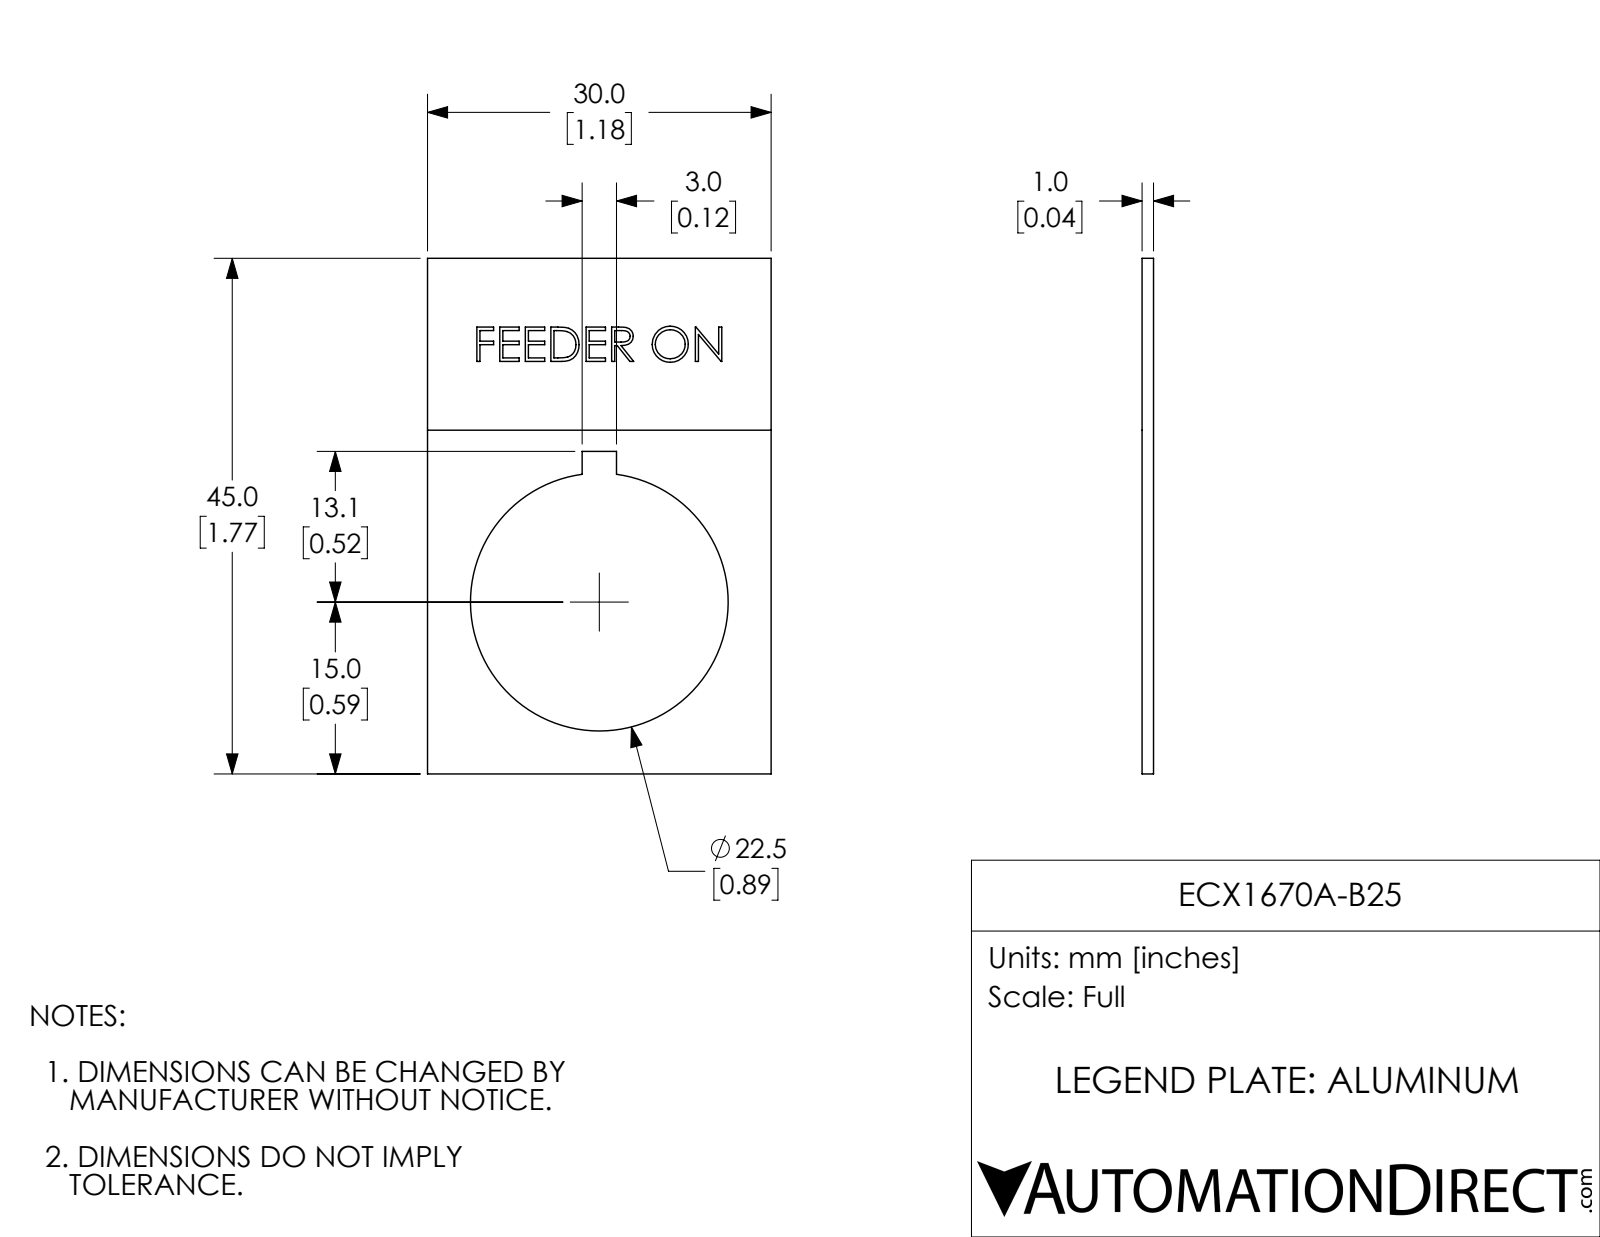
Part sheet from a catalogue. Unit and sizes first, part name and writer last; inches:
Units: inches
Overall size (bounding box): 1.772 × 1.181 × 0.039
Round holes (diameter × count): ⌀0.886 ×1
Main face-to-face distances: 0.039, 1.181, 1.772, 0.038, 0.531, 0.65, 1.108, 0.663, 0.118, 0.012
Volume: 0.058 in³ · Surface area: 3.288 in²
Bodies: 1 solid, 117 faces (94 planar, 3 cylindrical, 20 other)
Part name (STEP PRODUCT): ECX1670A-B25
STEP written by: SolidWorks 2017 (AUTOMOTIVE_DESIGN)
